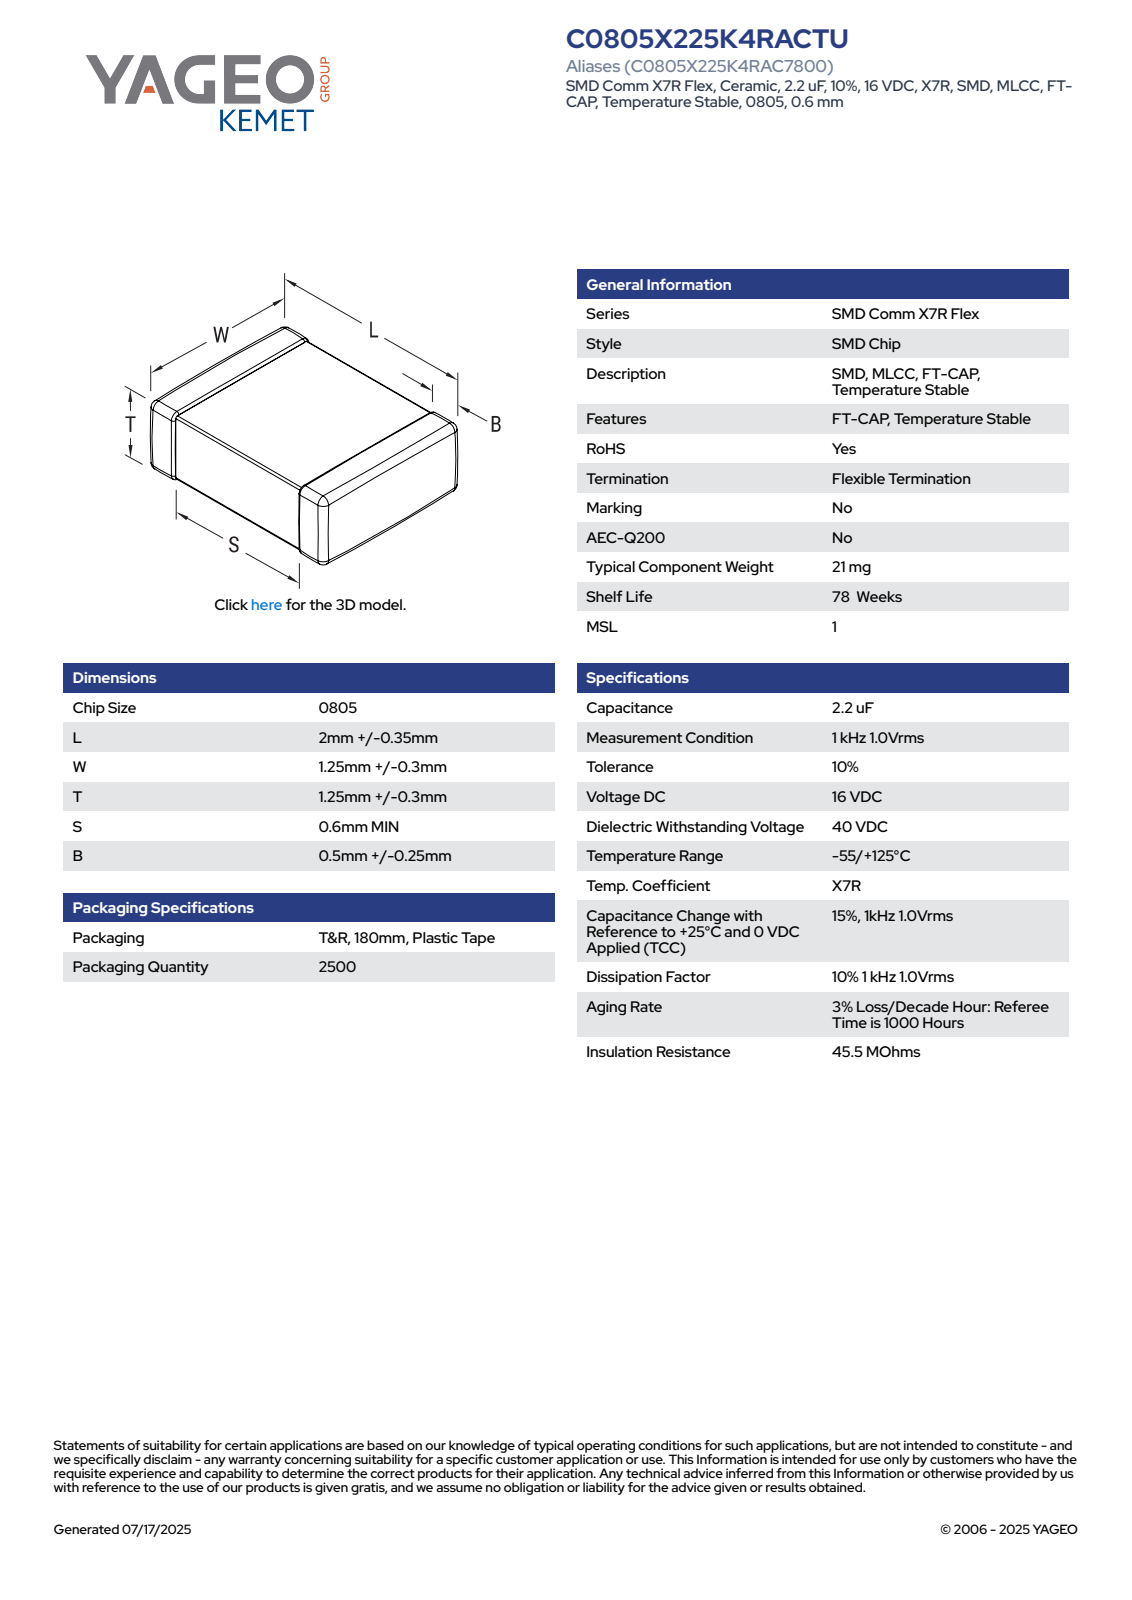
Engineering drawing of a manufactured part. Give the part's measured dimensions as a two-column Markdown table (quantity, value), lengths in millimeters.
| quantity | value |
| --- | --- |
| part name | CCS_CCSTD_0805_L2.35W1.55T1.55B0.5 |
| STEP written by | SolidWorks 2021 (AUTOMOTIVE_DESIGN) |
| units | millimeters |
| bodies | 4 solids, 125 faces (71 planar, 38 cylindrical, 16 other) |
| overall size | 2.35 × 1.55 × 1.55 |
| volume | 5 mm³ |
| surface area | 19 mm² |
| main face-to-face distances | 1.52, 1.55, 1.49, 2.35, 1.04, 1.31, 1.08, 1.27, 0.93, 0.47 |
